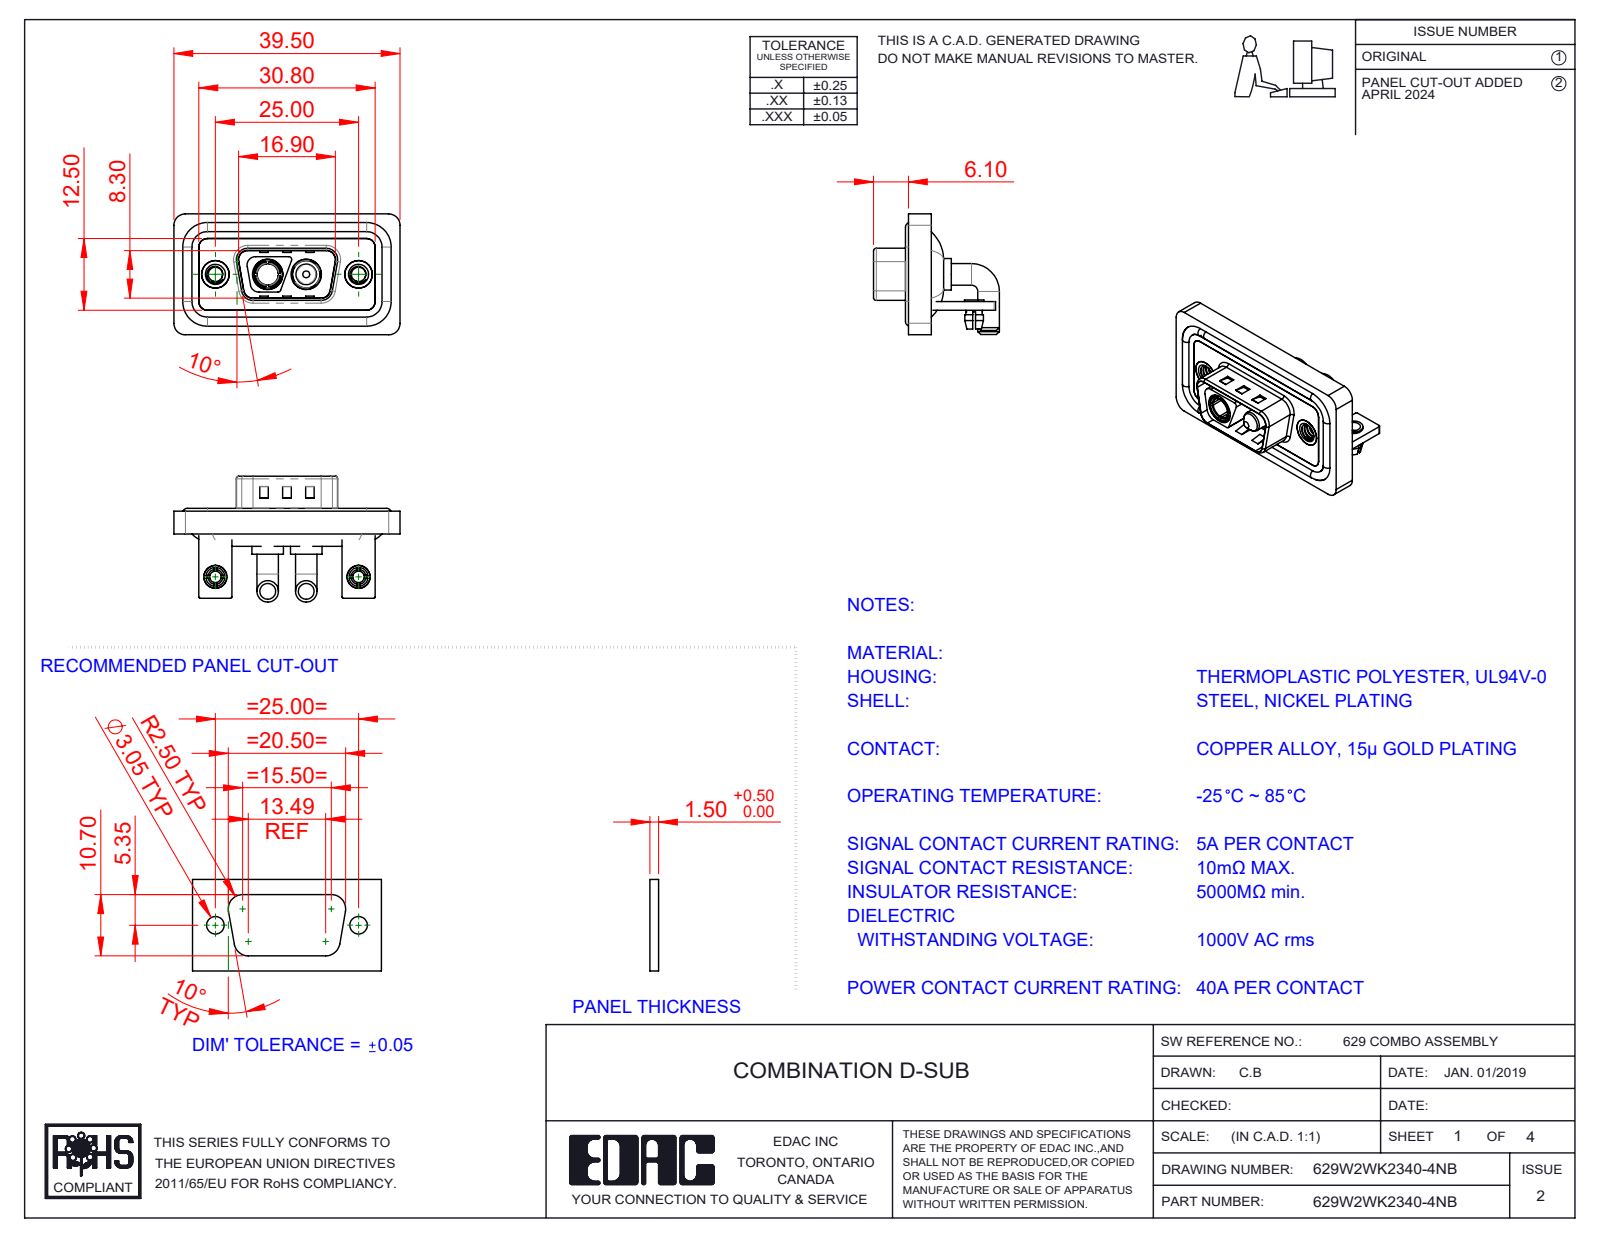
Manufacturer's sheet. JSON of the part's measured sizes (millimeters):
{"part_name": "629Combo Stabilizer Bracket; Power Socket_40A RA; 629Combo Waterproof Housing_09 Contacts; 629Combo Threaded Rivet_B (+6 more)", "step_written_by": "SolidWorks 2023 (CONFIG_CONTROL_DESIGN)", "units": "millimeters", "bodies": {"solids": 15, "faces": 672, "planar": 257, "cylindrical": 281, "other": 134}, "overall_size": [39.5, 21.98, 21.1], "volume_mm3": 5140, "surface_area_mm2": 8420, "round_holes": [[2.5, 4], [2, 2], [3.2, 2], [4, 2], [4.8, 2], [4.85, 2], [5, 2], [5.3, 2], [3.7, 1]], "round_bosses_or_shafts": [[3.75, 4], [1.6, 4], [5.5, 2], [5.2, 2], [4.9, 2], [4.75, 2], [4, 2], [3.4, 2]], "partial_cylinders_radius": [[1.5, 20], [2, 19], [0.25, 16], [0.5, 11], [1.6, 8], [0.6, 4], [0.65, 4], [0.9, 4]], "face_to_face_distances": [0.4, 1.5, 2.9, 0.8, 1.1, 1.2, 2.1, 1.6, 3.7, 2.5], "hole_center_spacings": [9.14, 15.86, 25, 6.72]}
